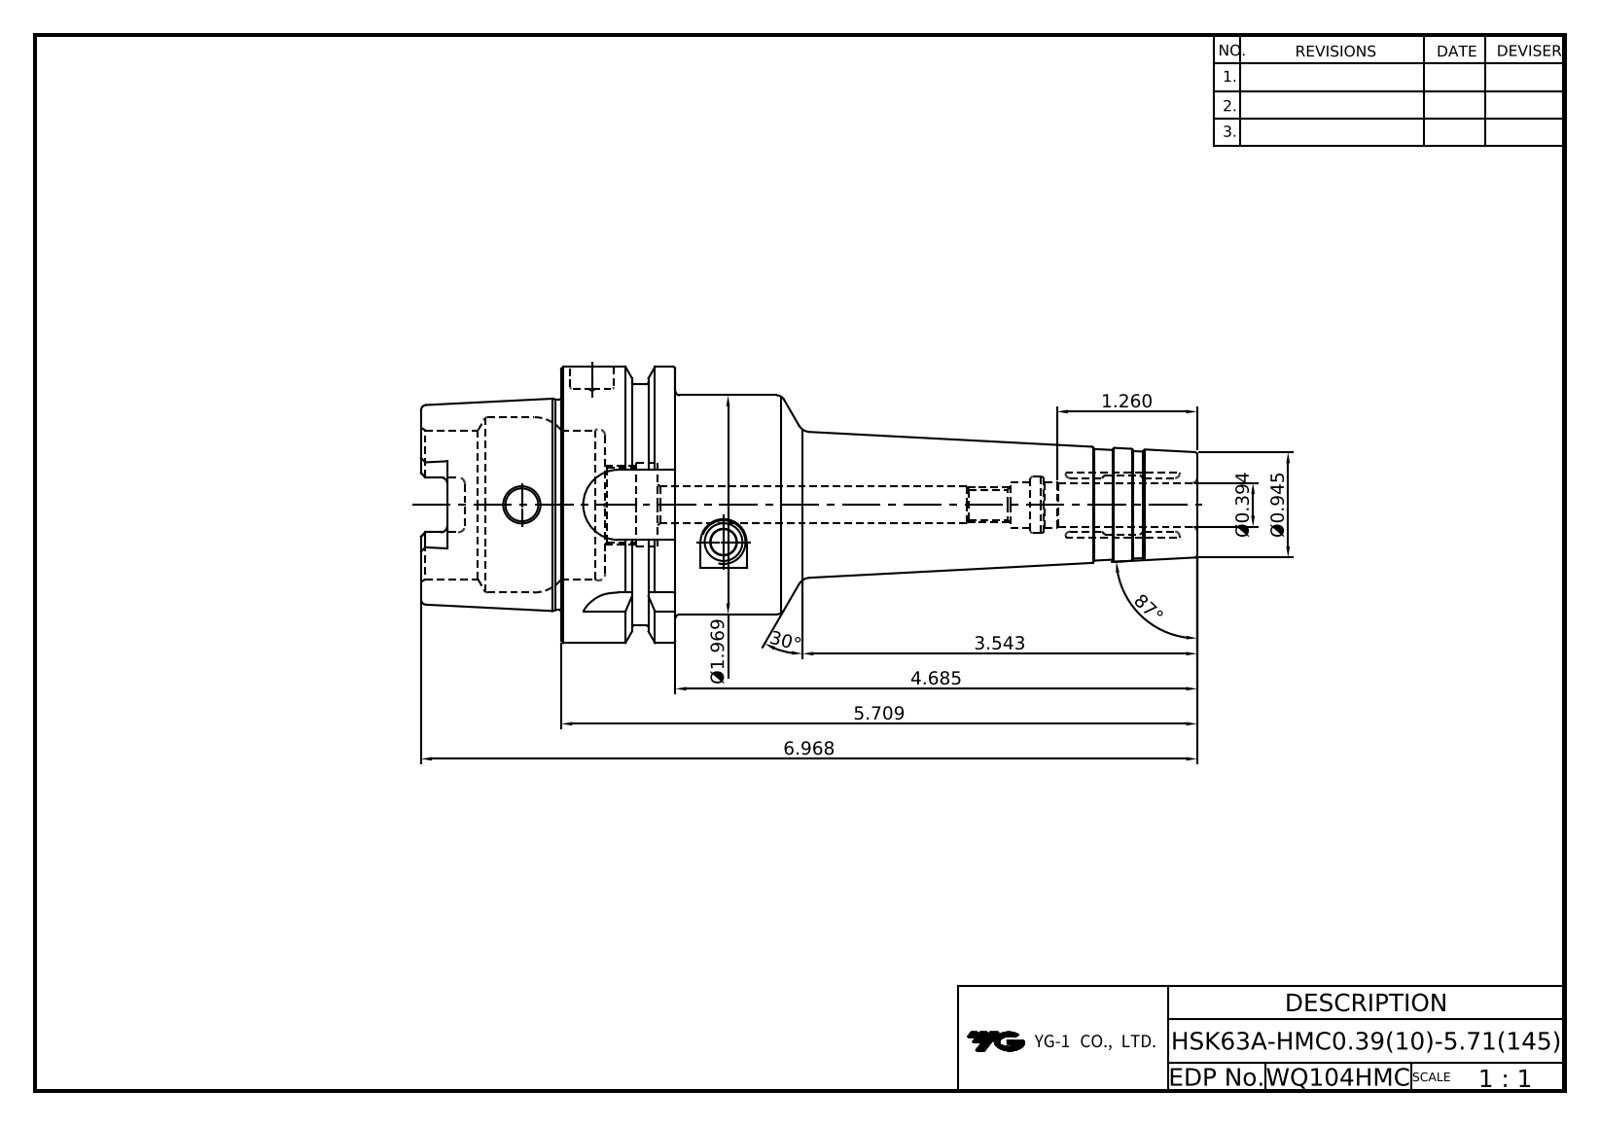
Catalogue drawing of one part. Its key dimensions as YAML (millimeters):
part_name: "HSK63A-HMC10-145"
step_written_by: "CREO PARAMETRIC BY PTC INC, 2018100 (CONFIG_CONTROL_DESIGN)"
units: millimeters
bodies: {solids: 1, faces: 183, planar: 56, cylindrical: 51, other: 76}
overall_size: [177, 63, 63]
volume: 187012
surface_area: 37708
round_holes:
  - {diameter: 10, count: 2}
  - {diameter: 7.5, count: 1}
  - {diameter: 8, count: 1}
  - {diameter: 8.4, count: 1}
  - {diameter: 10.4, count: 1}
  - {diameter: 17, count: 1}
  - {diameter: 18, count: 1}
  - {diameter: 19, count: 1}
  - {diameter: 34, count: 1}
  - {diameter: 40, count: 1}
round_bosses_or_shafts:
  - {diameter: 63, count: 1}
  - {diameter: 55, count: 1}
  - {diameter: 50, count: 1}
  - {diameter: 48.04, count: 1}
partial_cylinders:
  - {radius: 1.5, count: 6}
  - {radius: 2.88, count: 4}
  - {radius: 8, count: 4}
face_to_face_distances: [26, 10, 16, 32, 6.12, 9.88, 42, 58, 4, 22]
